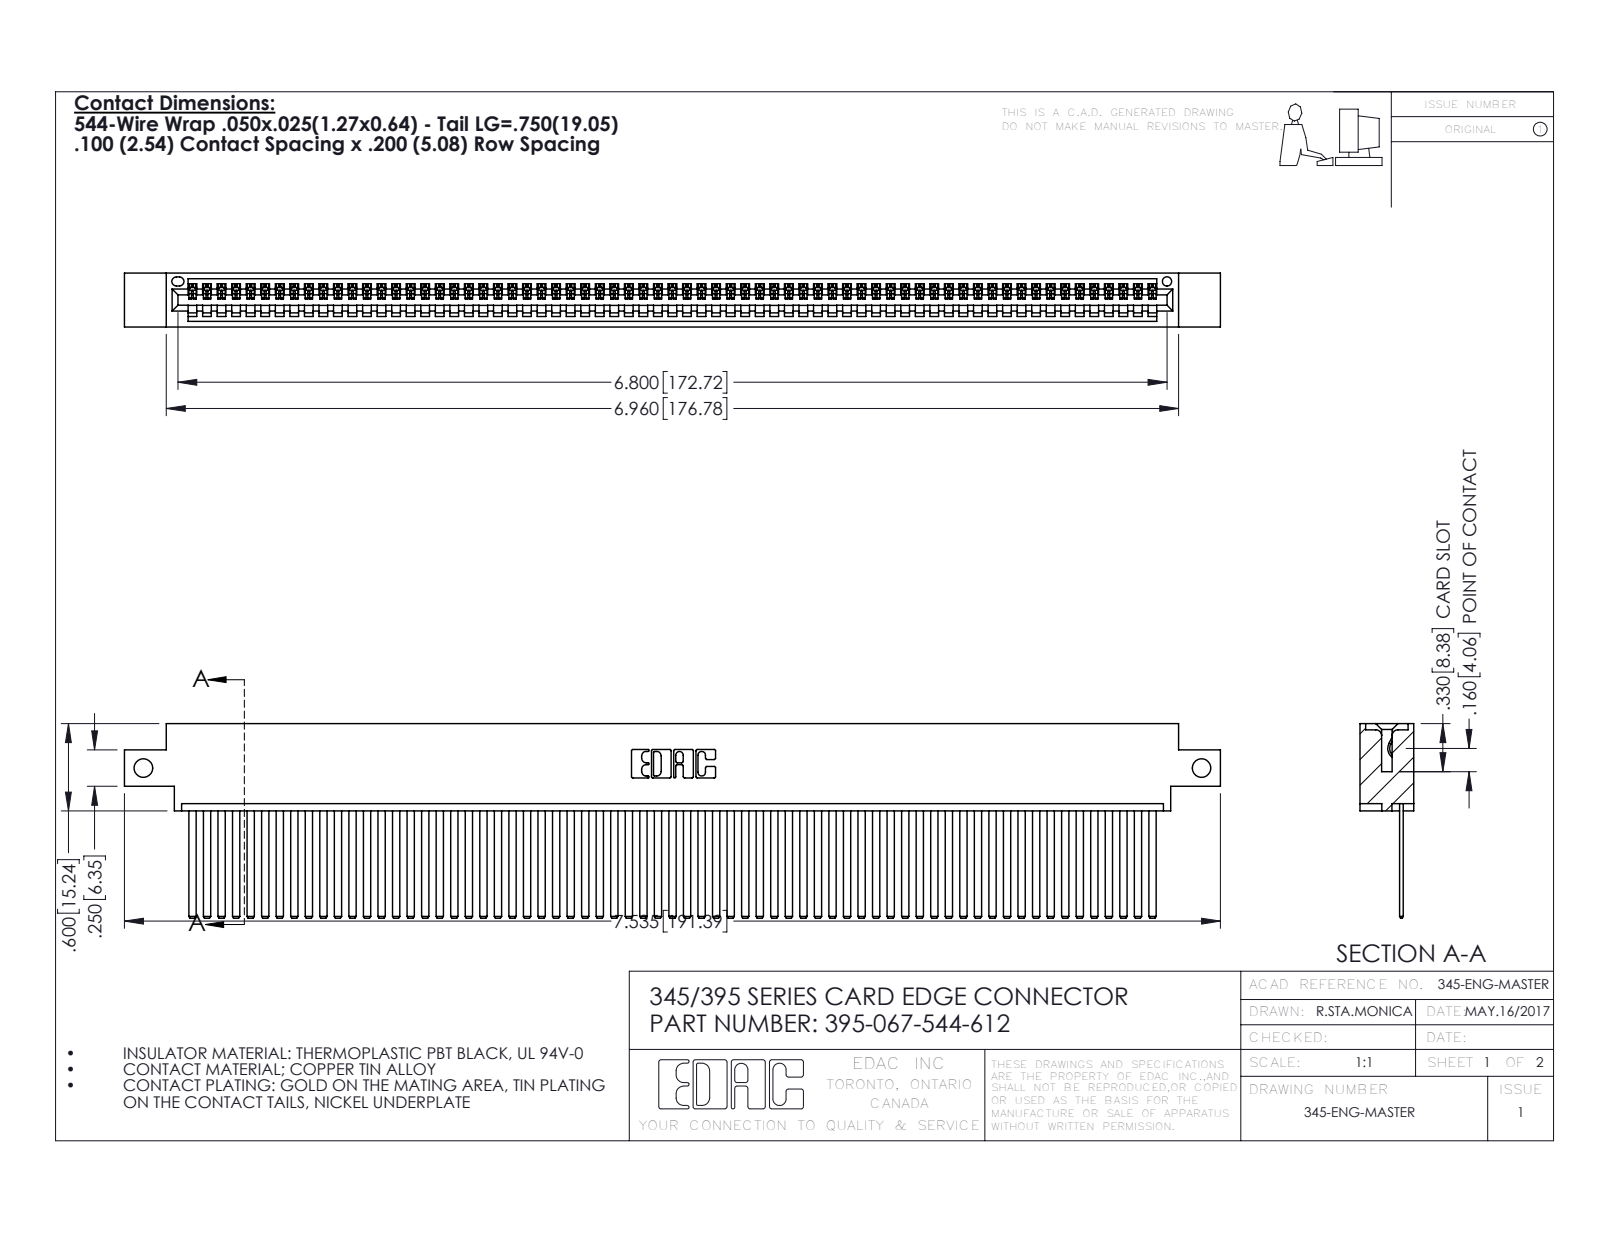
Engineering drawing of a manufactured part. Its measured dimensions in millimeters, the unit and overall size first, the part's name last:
Units: millimetres
Overall size (bounding box): 191.4 × 34 × 9.4
Round holes (diameter × count): ⌀3.3 ×2, ⌀1.6 ×1
Partial cylindrical surfaces — rounded edges, fillets, slot ends (radius × count): R0.2 ×134, R0.3 ×22, R0.2 ×6, R0.8 ×6, R0.7 ×3, R0.8 ×2, R1 ×2, R0.4 ×1
Main face-to-face distances: 1.8, 7.6, 0.6, 2.5, 6.9, 9.4, 5.1, 5.7, 4.4, 3.8
Hole centre spacings: 184.8
Volume: 18 960 mm³ · Surface area: 27 850 mm²
Bodies: 68 solids, 3614 faces (2496 planar, 1118 cylindrical, 0 other)
Part name (STEP PRODUCT): 345-292-001_345-293-144; 395-067-544-612; 345 Part_0.170 Offset - Side Mount
STEP written by: SolidWorks 2016 (CONFIG_CONTROL_DESIGN)
